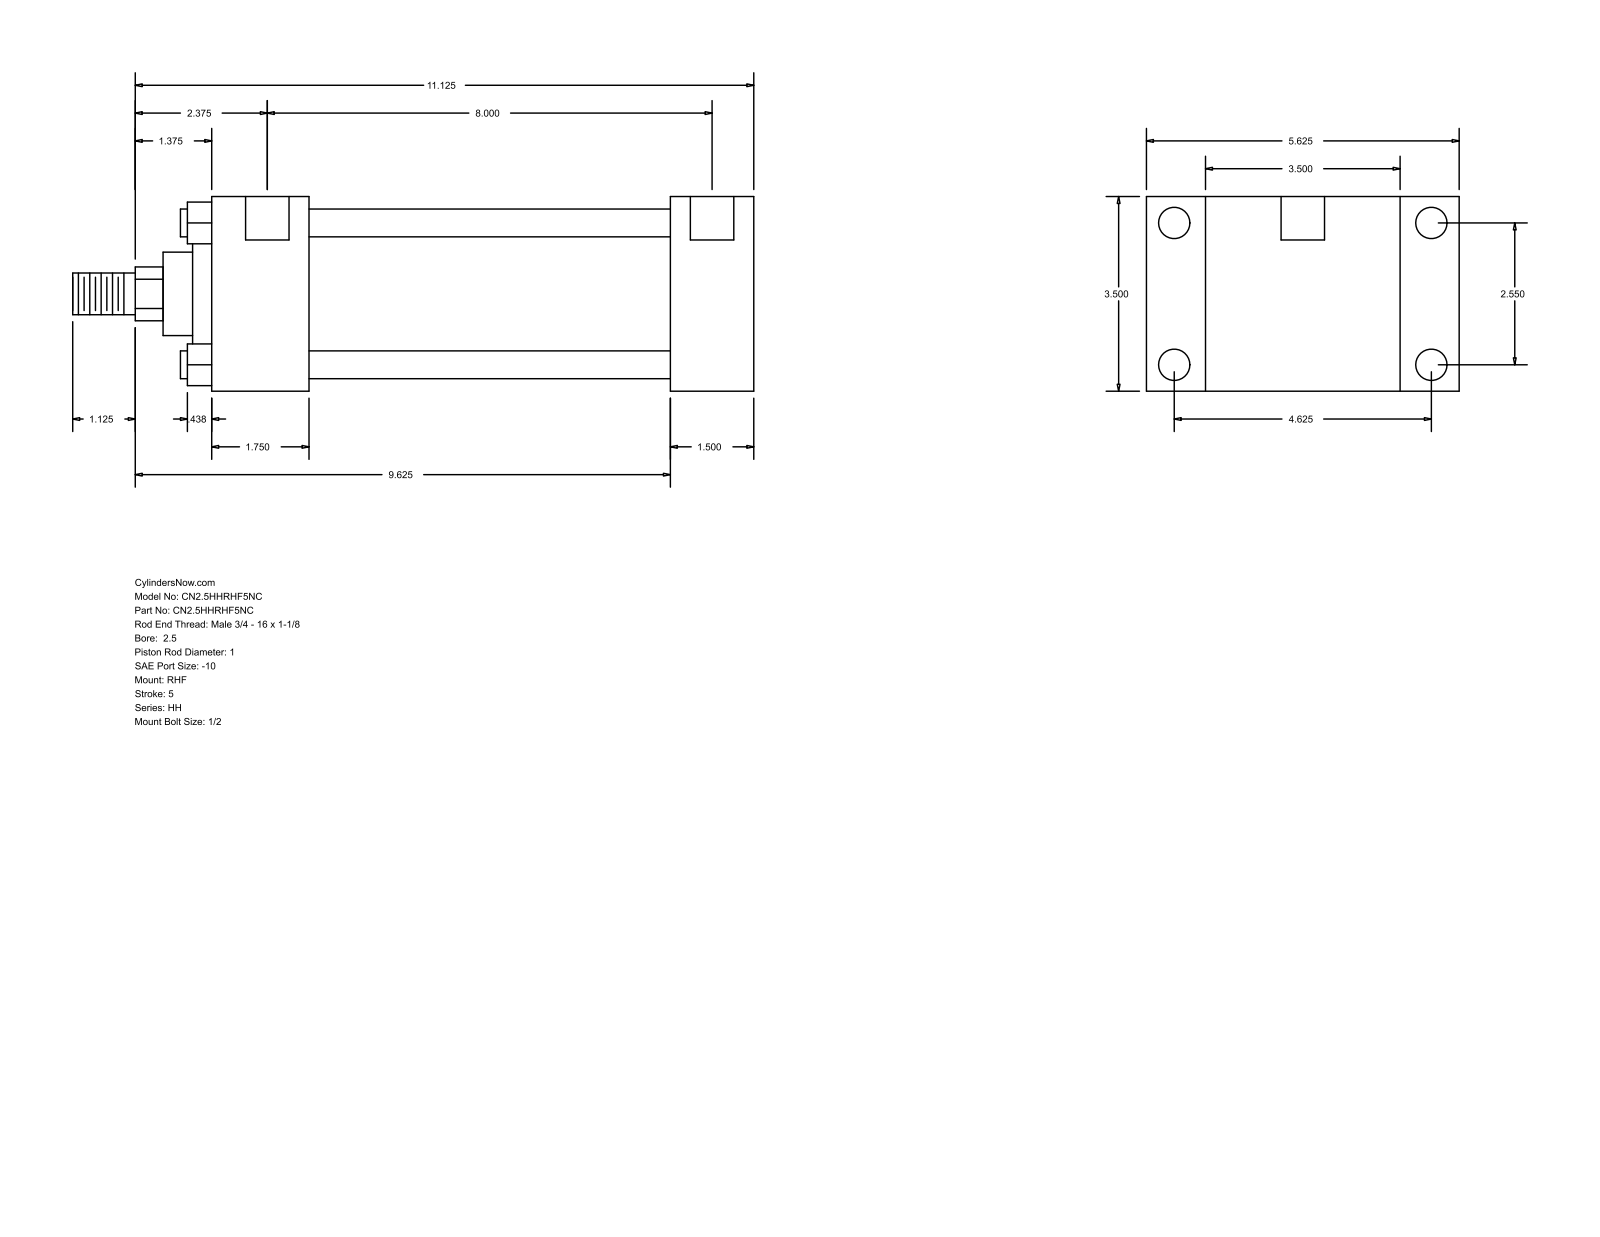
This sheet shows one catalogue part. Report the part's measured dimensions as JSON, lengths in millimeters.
{"part_name": "HH_RHF__0250_1", "step_written_by": "GSSL Pune (CONFIG_CONTROL_DESIGN)", "units": "millimeters", "bodies": {"solids": 0, "faces": 90, "planar": 61, "cylindrical": 29, "other": 0}, "overall_size": [311.15, 142.88, 88.9], "round_holes": [[5.56, 4], [14.3, 4], [19.84, 2]], "round_bosses_or_shafts": [[12.7, 4], [73.03, 1], [60.33, 1], [38.1, 1], [25.4, 1], [19.05, 1]], "partial_cylinders_radius": [[12.29, 1]], "face_to_face_distances": [88.9, 38.1, 26.99, 115.89, 209.55, 247.65, 142.88, 44.46, 165.09, 203.19], "hole_center_spacings": [1.59, 64.76, 117.48, 134.15, 204.78, 206.37, 203.19]}
